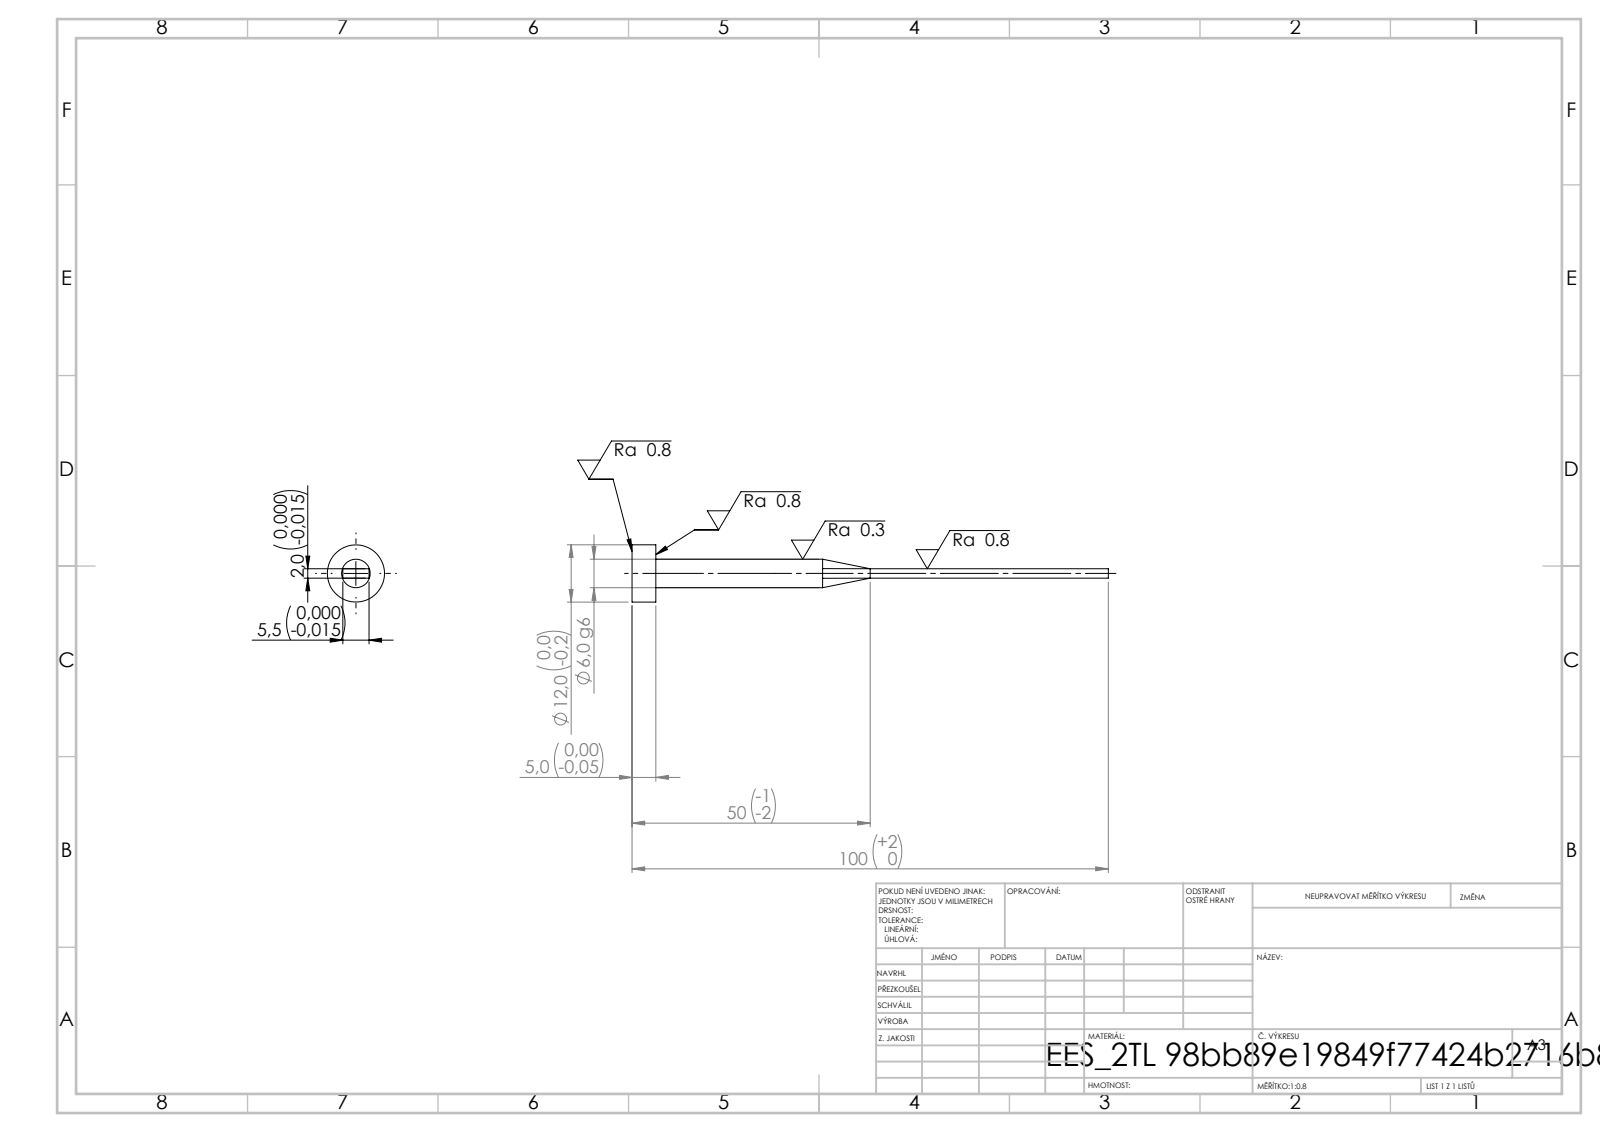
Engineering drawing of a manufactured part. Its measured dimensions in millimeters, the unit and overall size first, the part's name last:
Units: millimetres
Overall size (bounding box): 100 × 12 × 12
Round bosses / shafts (diameter × count): ⌀12 ×1, ⌀6 ×1
Main face-to-face distances: 2, 5.5, 5, 100, 95
Volume: 2 297 mm³ · Surface area: 1 972 mm²
Bodies: 1 solid, 15 faces (7 planar, 4 cylindrical, 4 other)
STEP written by: SolidWorks 2019 (CONFIG_CONTROL_DESIGN)
